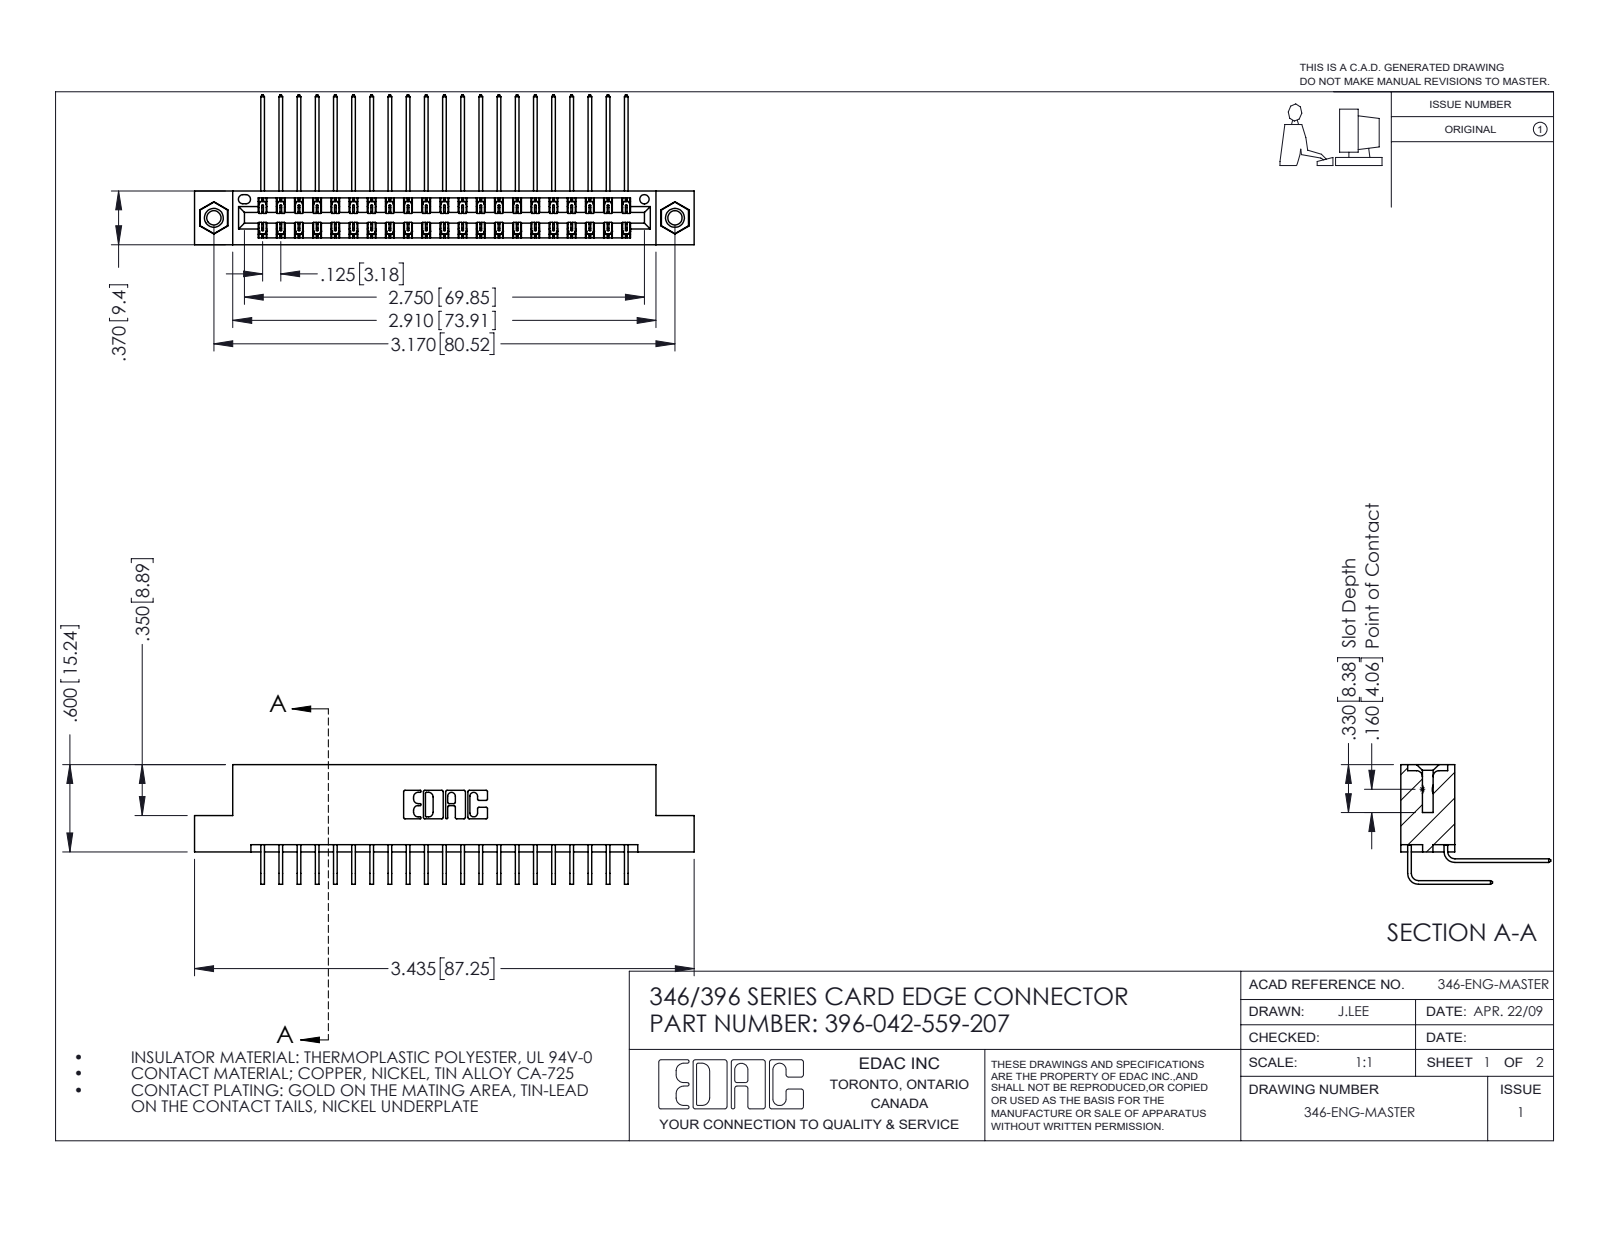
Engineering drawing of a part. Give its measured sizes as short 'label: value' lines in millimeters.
name: 345-292-001_558 559 Tail - 1; 346 Part_Flush Mounting Lugs - 0.156 Dia-TI; 345-292-001_559 Tail - 2; 396-042-559-207 (+1 more)
written by: SolidWorks 2016 (CONFIG_CONTROL_DESIGN)
unit: mm
bodies: 45 solids, 2450 faces (1662 planar, 772 cylindrical, 16 other)
size: 87.2 × 26.2 × 20.9
volume: 8 570 mm³; area: 12 650 mm²
holes: 2× ⌀2.5, 2× ⌀3.2, 2× ⌀4, 1× ⌀1.6
bosses: 2× ⌀3.9
rounds: 63× R0.2, 22× R0.3, 6× R0.2, 6× R0.8, 3× R0.7, 2× R0.4, 2× R0.6, 2× R0.6
face distances: 1.2, 8.2, 6.4, 0.6, 9.4, 1.8, 7.6, 7, 3.8, 5.6
hole spacings: 6.2, 75.3, 80.5
